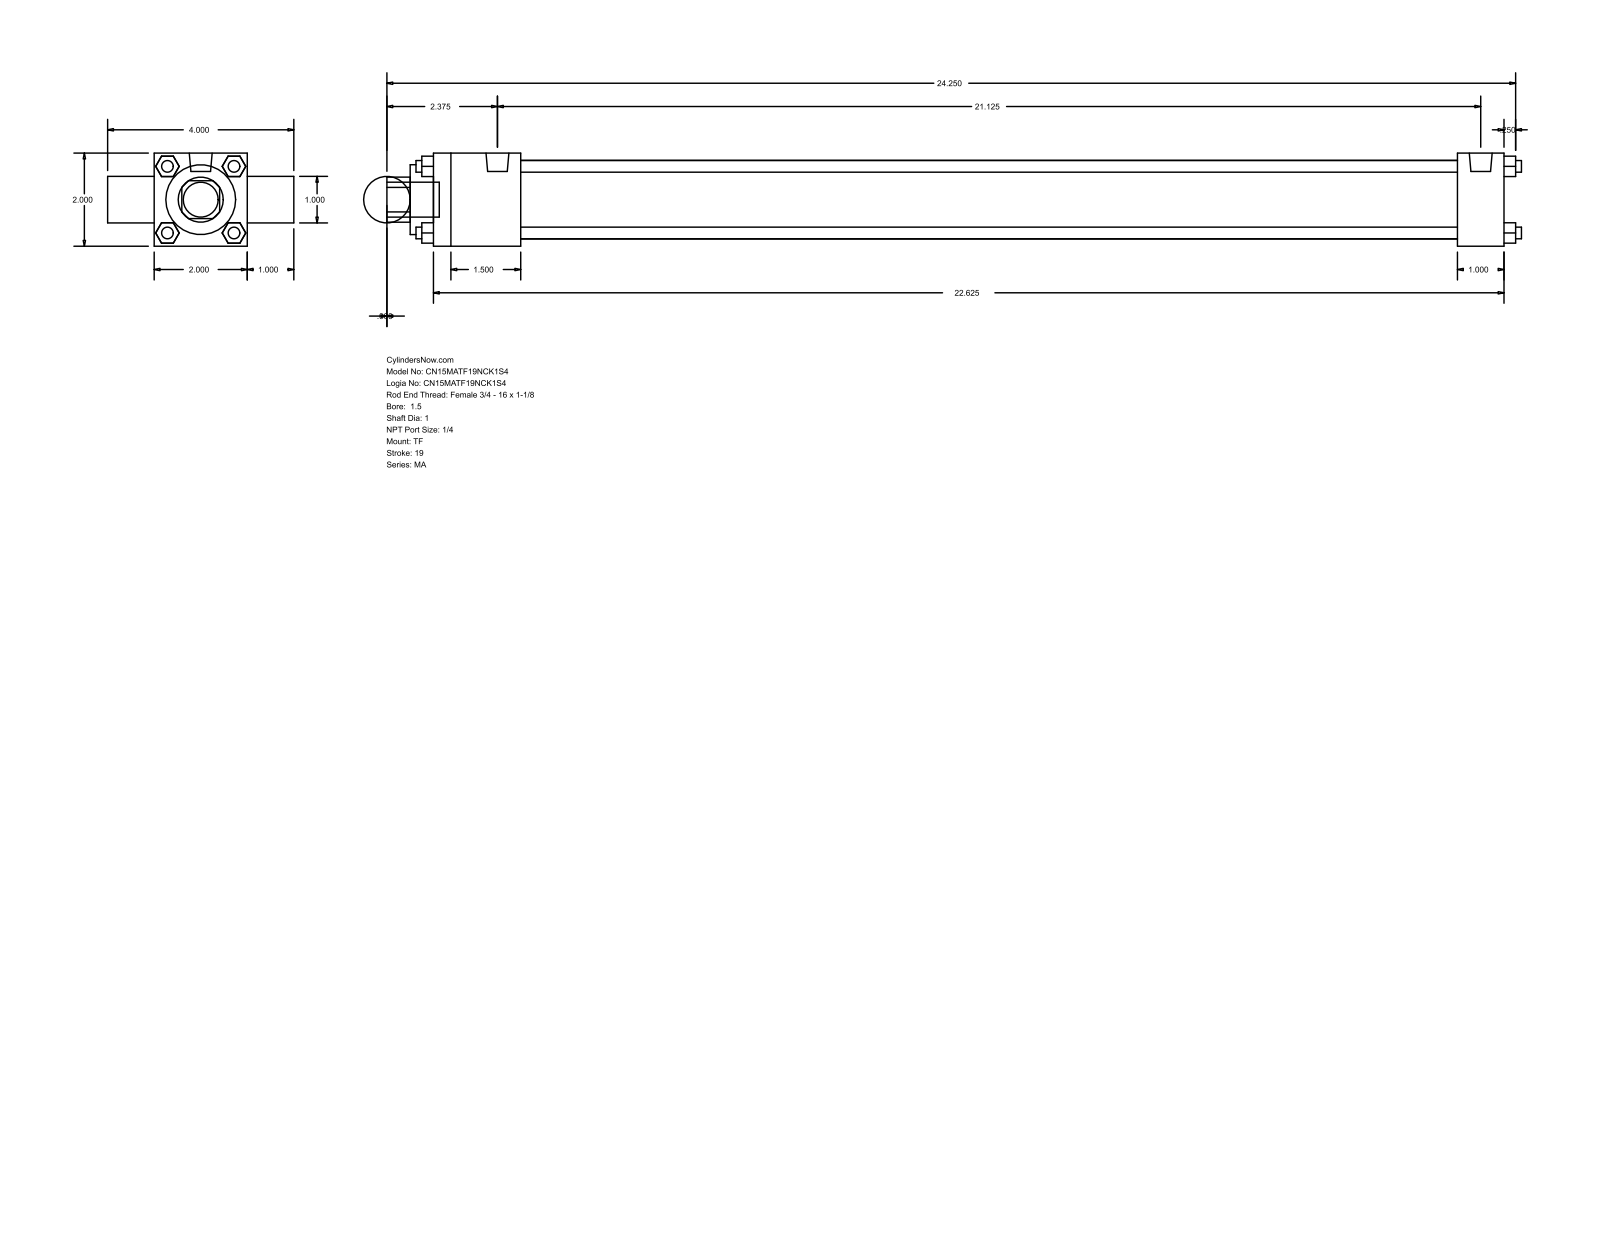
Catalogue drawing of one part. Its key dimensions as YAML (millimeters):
part_name: "MA_TF__0150_1"
step_written_by: "GSSL Pune (CONFIG_CONTROL_DESIGN)"
units: millimeters
bodies: {solids: 0, faces: 120, planar: 92, cylindrical: 28, other: 0}
overall_size: [619.12, 101.6, 50.8]
round_holes:
  - {diameter: 25.4, count: 2}
  - {diameter: 38.1, count: 1}
  - {diameter: 42.93, count: 1}
round_bosses_or_shafts:
  - {diameter: 6.35, count: 4}
  - {diameter: 7.94, count: 3}
  - {diameter: 12.49, count: 2}
  - {diameter: 19.05, count: 1}
partial_cylinders:
  - {radius: 12.29, count: 1}
face_to_face_distances: [50.8, 25.4, 584.2, 76.2, 6.35, 47.63, 558.8, 511.17, 536.57, 596.9]
